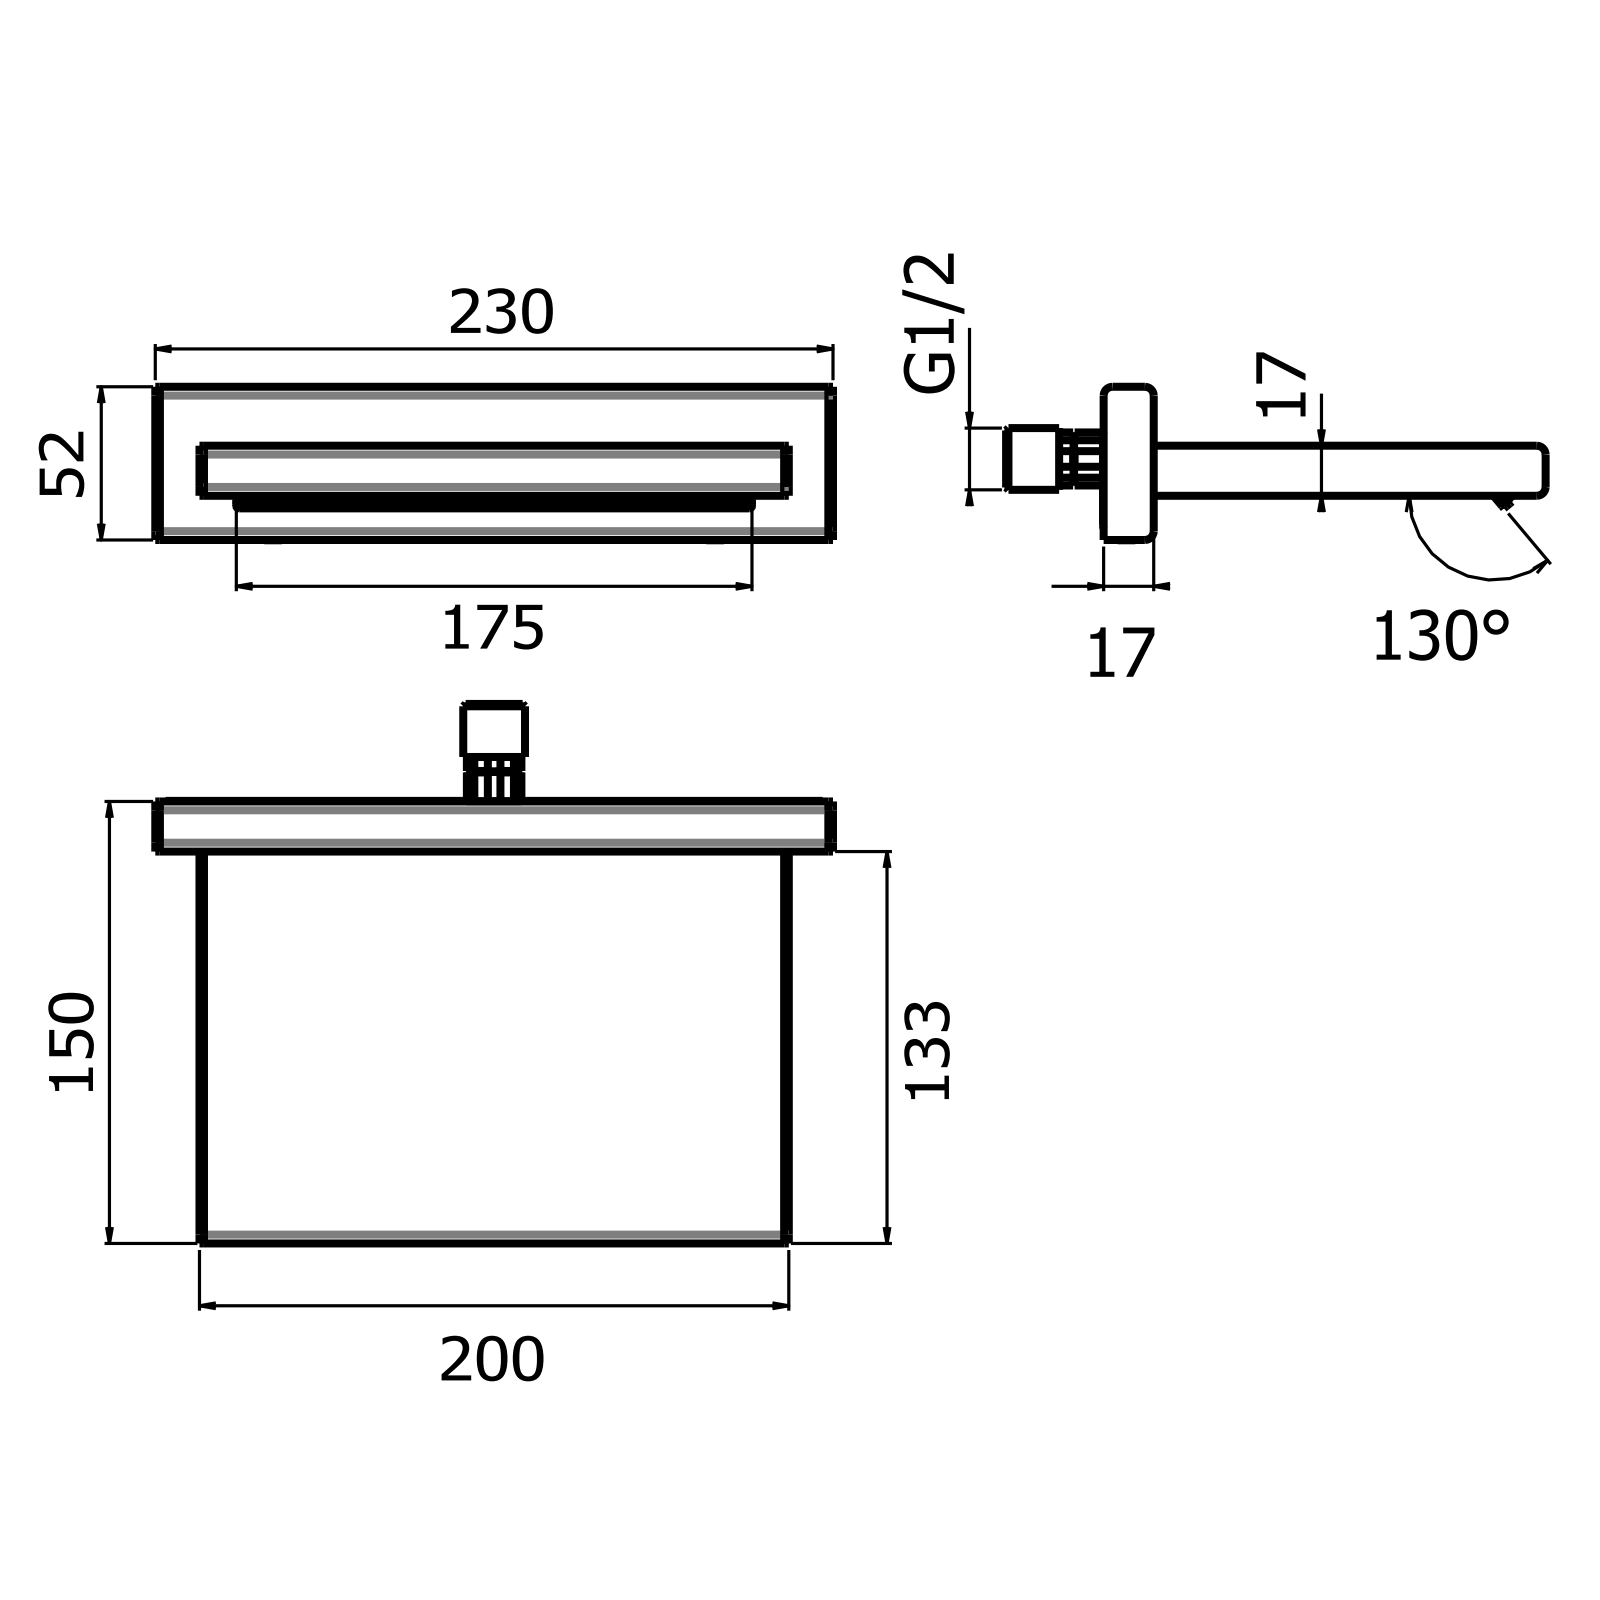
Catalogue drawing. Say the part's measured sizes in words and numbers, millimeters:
The part is named "A.R._24529/20220905". Its 3-D file was written by "Spatial InterOp 3D (AUTOMOTIVE_DESIGN)". It is 1 solid with 305 faces: 192 planar, 87 cylindrical and 26 other. Overall it measures 230 by 173.2 by 52.1 millimeters. Its volume is 203 274 cubic millimeters and its surface area 251 398 square millimeters. Round holes: 2 of diameter 2.5, 2 of diameter 3.2, 2 of diameter 4, 2 of diameter 4.4, 1 of diameter 8, 1 of diameter 9. Round bosses or shafts: 2 of diameter 6, 2 of diameter 4.9, 2 of diameter 3, 2 of diameter 2.8, 1 of diameter 14.8, 1 of diameter 10.8. Partial cylindrical surfaces (rounded edges, fillets, slot ends): 10 of radius 1.5, 10 of radius 3, 9 of radius 2, 8 of radius 2.25, 6 of radius 20, 3 of radius 1, 2 of radius 288.33, 1 of radius 2.5. The main face-to-face distances are 1.5, 2.5, 13, 15.5, 17, 1, 11.5, 12, 10.5, 5. The hole center spacings are 75.02, 94.33, 150, 188.5.
